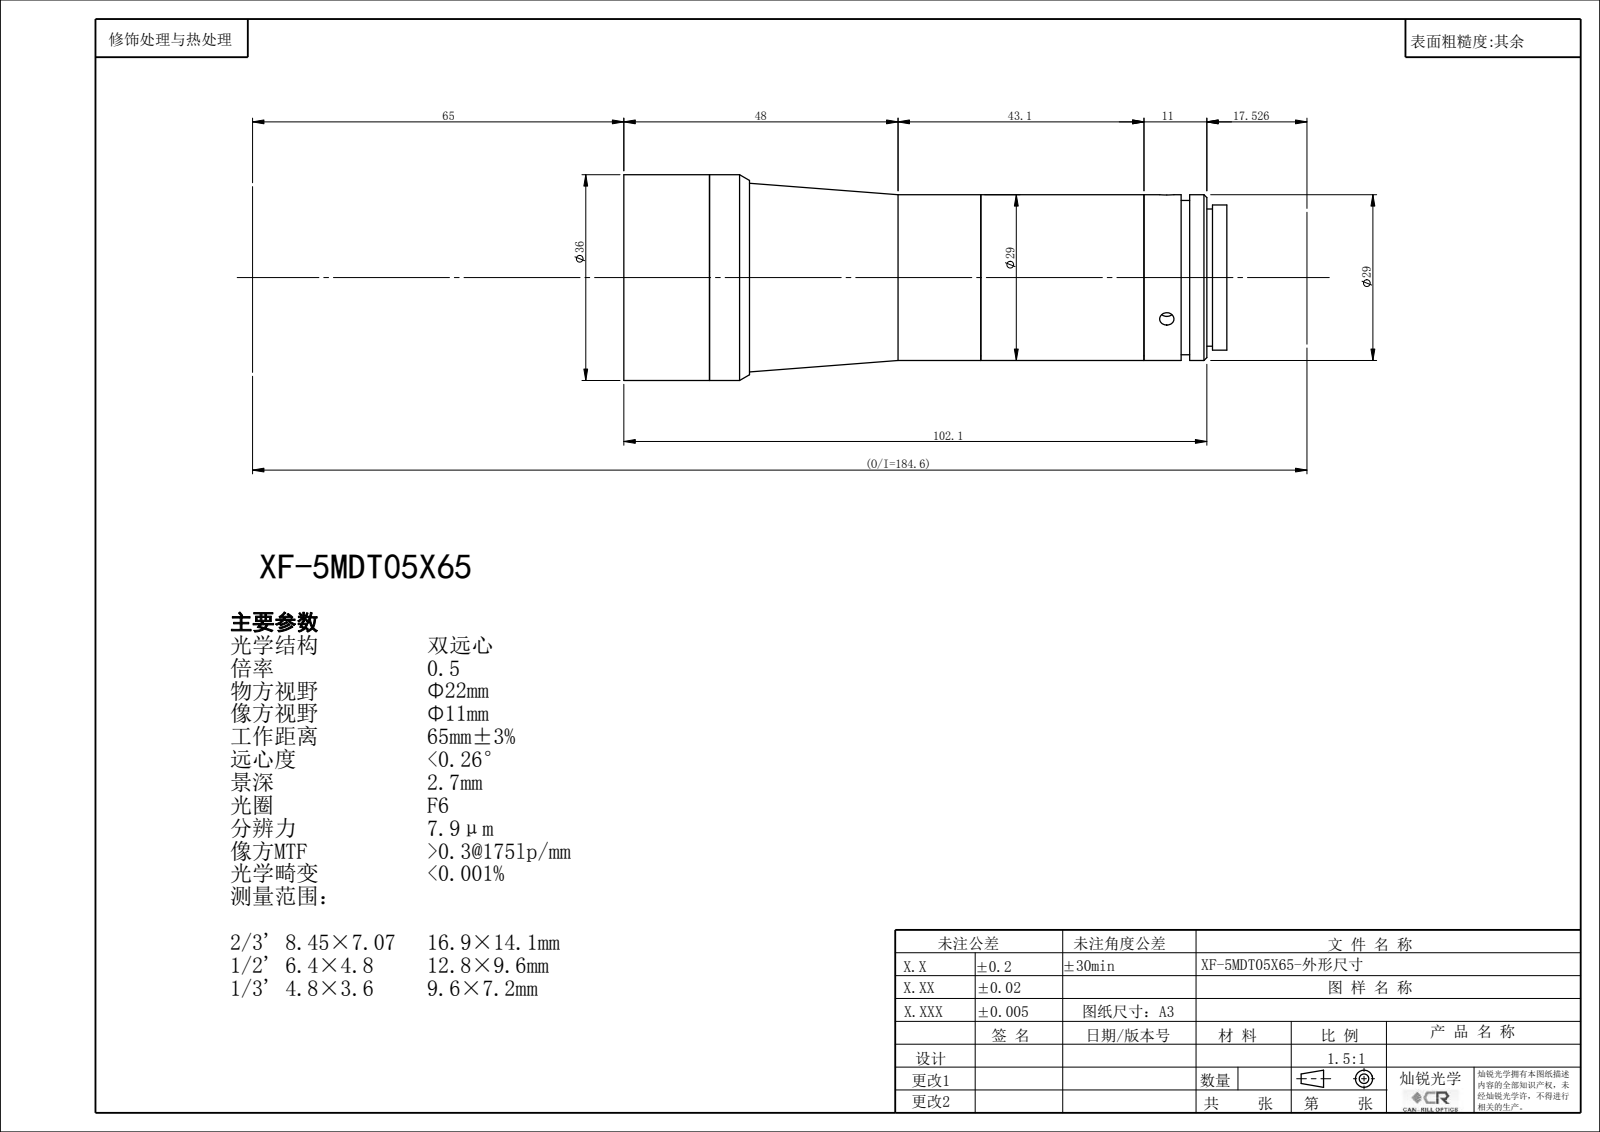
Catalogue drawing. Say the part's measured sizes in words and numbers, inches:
Its 3-D file was written by "SolidWorks 2014 (CONFIG_CONTROL_DESIGN)". It is 0 solids with 68 faces: 22 planar, 36 cylindrical and 10 other. Overall it measures 4.156 by 1.417 by 1.417 inches. Round holes: 3 of diameter 0.098, 1 of diameter 0.709, 1 of diameter 0.843, 1 of diameter 1.181, 1 of diameter 1.276. Round bosses or shafts: 1 of diameter 1.417, 1 of diameter 1.299, 1 of diameter 1.142, 1 of diameter 1.063, 1 of diameter 1, 1 of diameter 0.945, 1 of diameter 0.906. The main face-to-face distances are 2.994, 0.217, 0.591, 3.585, 0.256, 0.315, 4.018, 3.428, 0.433, 3.939.
